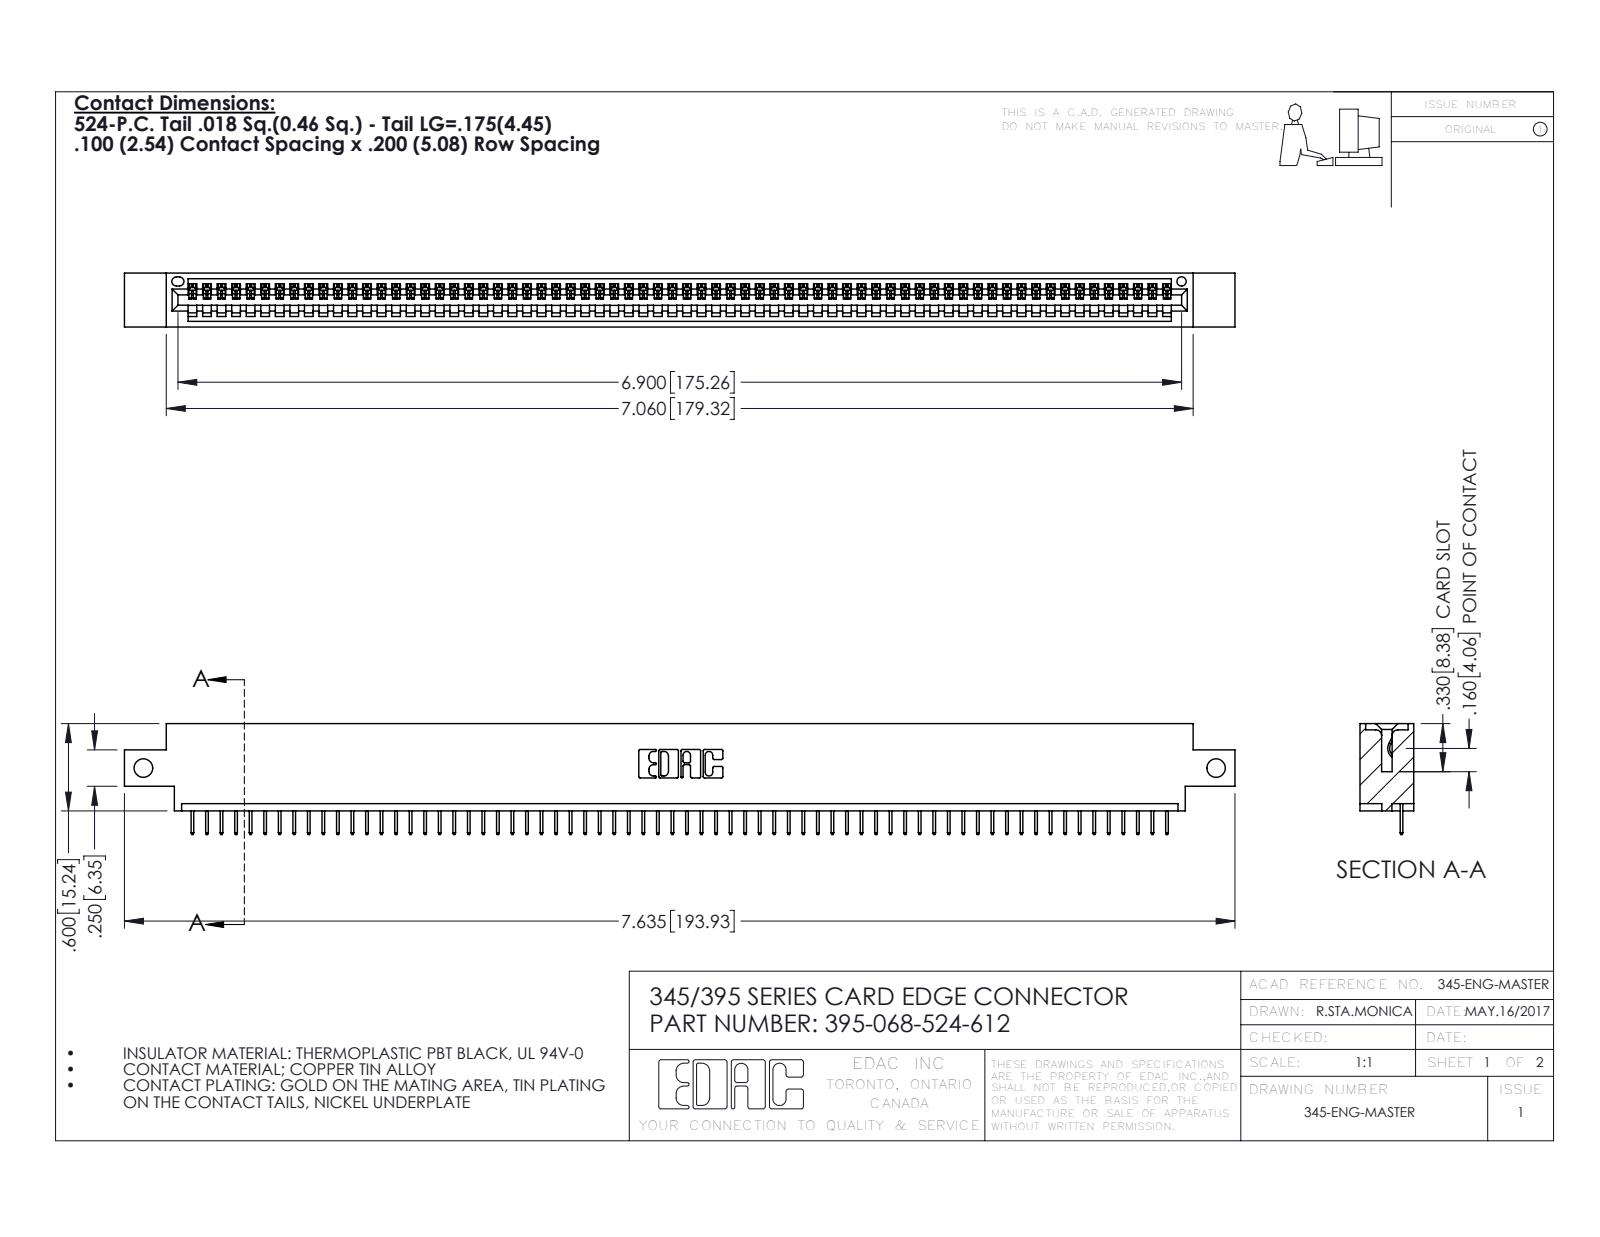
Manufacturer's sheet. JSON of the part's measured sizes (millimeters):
{"part_name": "345 Part_0.170 Offset - Side Mount; 395-068-524-612; 345-292-001_345-293-124", "step_written_by": "SolidWorks 2016 (CONFIG_CONTROL_DESIGN)", "units": "millimeters", "bodies": {"solids": 69, "faces": 4346, "planar": 3212, "cylindrical": 1134, "other": 0}, "overall_size": [193.9, 19.4, 9.4], "volume_mm3": 18160, "surface_area_mm2": 23620, "round_holes": [[3.3, 2], [1.6, 1]], "partial_cylinders_radius": [[0.2, 136], [0.3, 22], [0.2, 6], [0.8, 6], [0.7, 3], [0.8, 2], [1, 2], [0.4, 1]], "face_to_face_distances": [1.8, 7.6, 9.4, 5.1, 2.5, 6.9, 0.6, 5.7, 1.8, 4.4], "hole_center_spacings": [187.3]}
